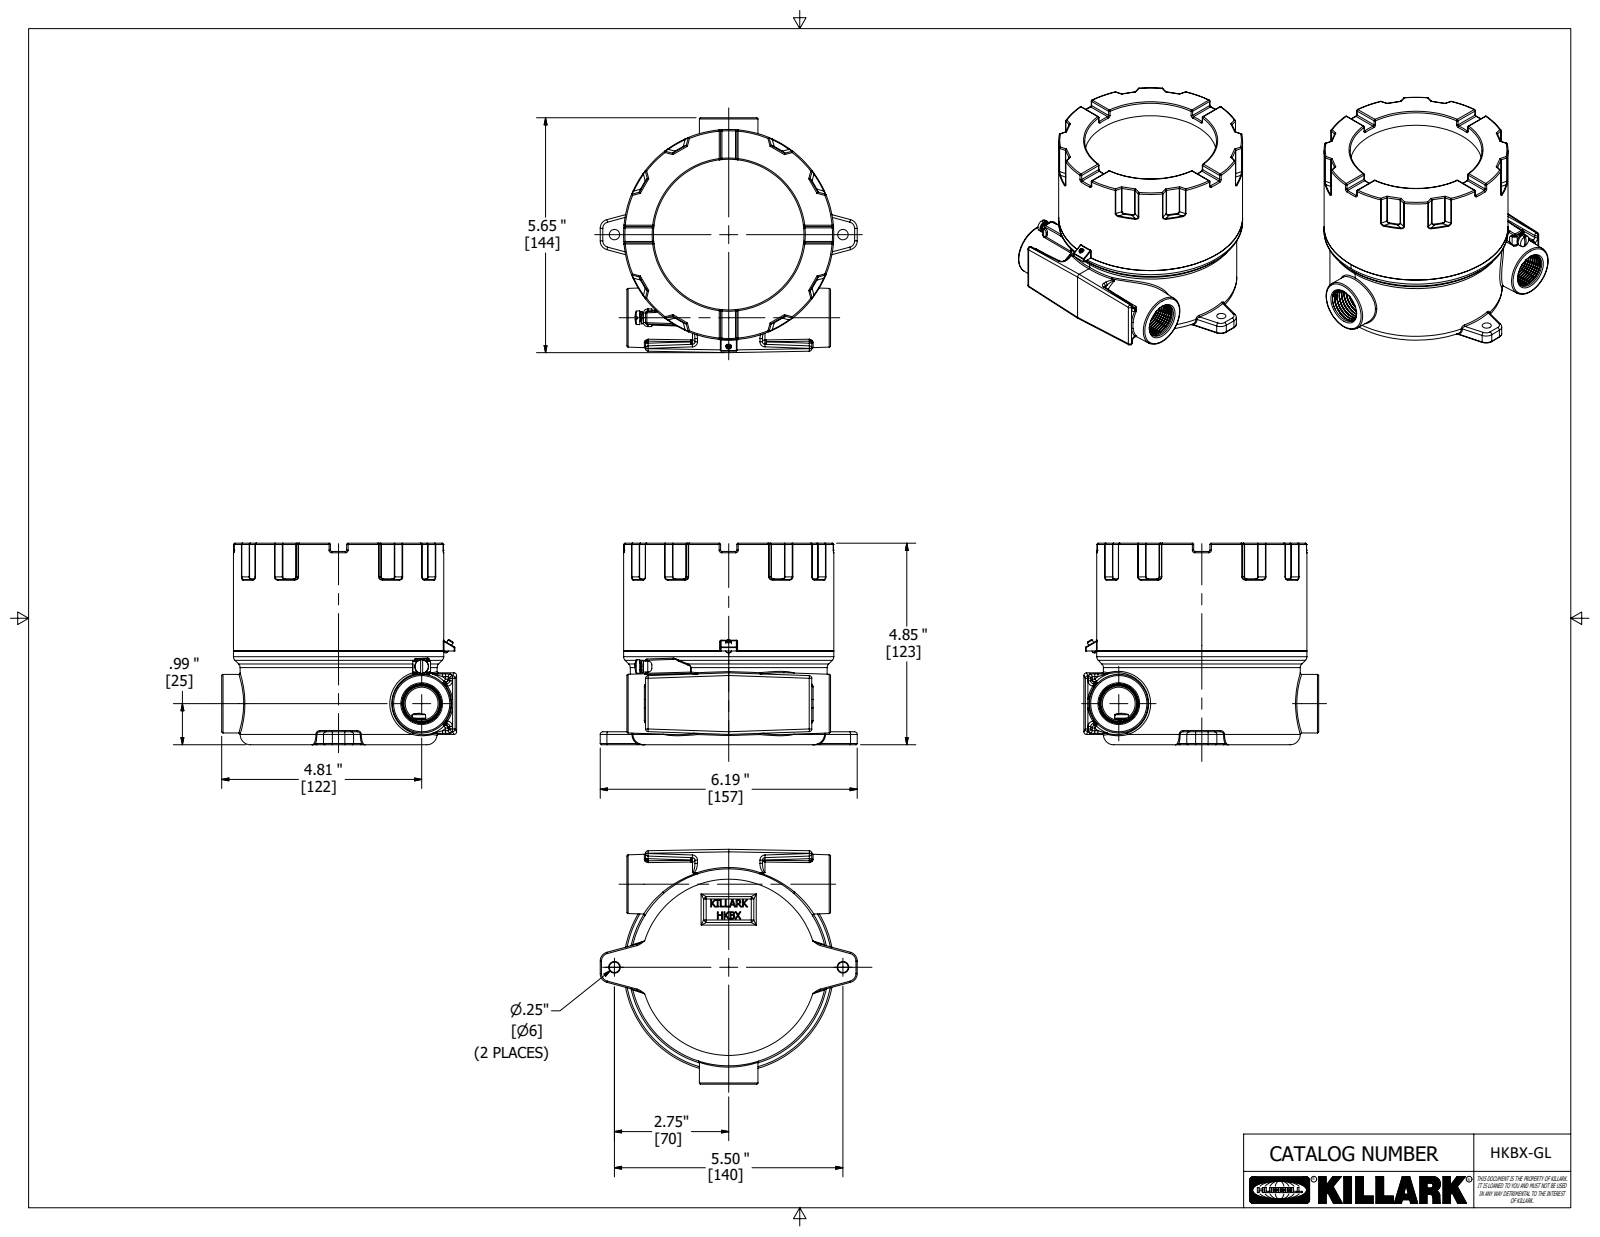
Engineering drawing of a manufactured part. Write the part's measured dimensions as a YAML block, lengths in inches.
part_name: "KIL_HKBX-GL; 51639ABAM for web; 51641ABAM for web; 51643AAAB (+7 more)"
step_written_by: "Autodesk Inventor 2020 (AUTOMOTIVE_DESIGN)"
units: inches
bodies: {solids: 16, faces: 1006, planar: 332, cylindrical: 259, other: 415}
overall_size: [24.949, 14.924, 4.852]
volume: 41.6
surface_area: 629
round_holes:
  - {diameter: 0.125, count: 4}
  - {diameter: 0.13, count: 2}
  - {diameter: 0.18, count: 2}
  - {diameter: 0.25, count: 2}
  - {diameter: 0.104, count: 1}
  - {diameter: 0.792, count: 1}
  - {diameter: 3.625, count: 1}
  - {diameter: 3.625, count: 1}
  - {diameter: 3.625, count: 1}
  - {diameter: 3.881, count: 1}
  - {diameter: 4.1, count: 1}
  - {diameter: 4.34, count: 1}
round_bosses_or_shafts:
  - {diameter: 0.293, count: 2}
  - {diameter: 0.158, count: 2}
  - {diameter: 5.06, count: 1}
  - {diameter: 4.74, count: 1}
  - {diameter: 4.724, count: 1}
  - {diameter: 4.585, count: 1}
  - {diameter: 4.331, count: 1}
  - {diameter: 4.204, count: 1}
partial_cylinders:
  - {radius: 0.031, count: 61}
  - {radius: 0.062, count: 51}
  - {radius: 0.016, count: 47}
  - {radius: 0.125, count: 8}
  - {radius: 0.05, count: 4}
  - {radius: 0.094, count: 4}
  - {radius: 0.1, count: 4}
  - {radius: 0.219, count: 4}
face_to_face_distances: [4.399, 4.024, 0.375, 0.25, 4.149, 3.774, 0.014, 4.852, 4.602, 0.827]
hole_center_spacings: [2.869, 2.028, 2.029, 2.75, 3.258, 3.361, 4.057, 0.212]
